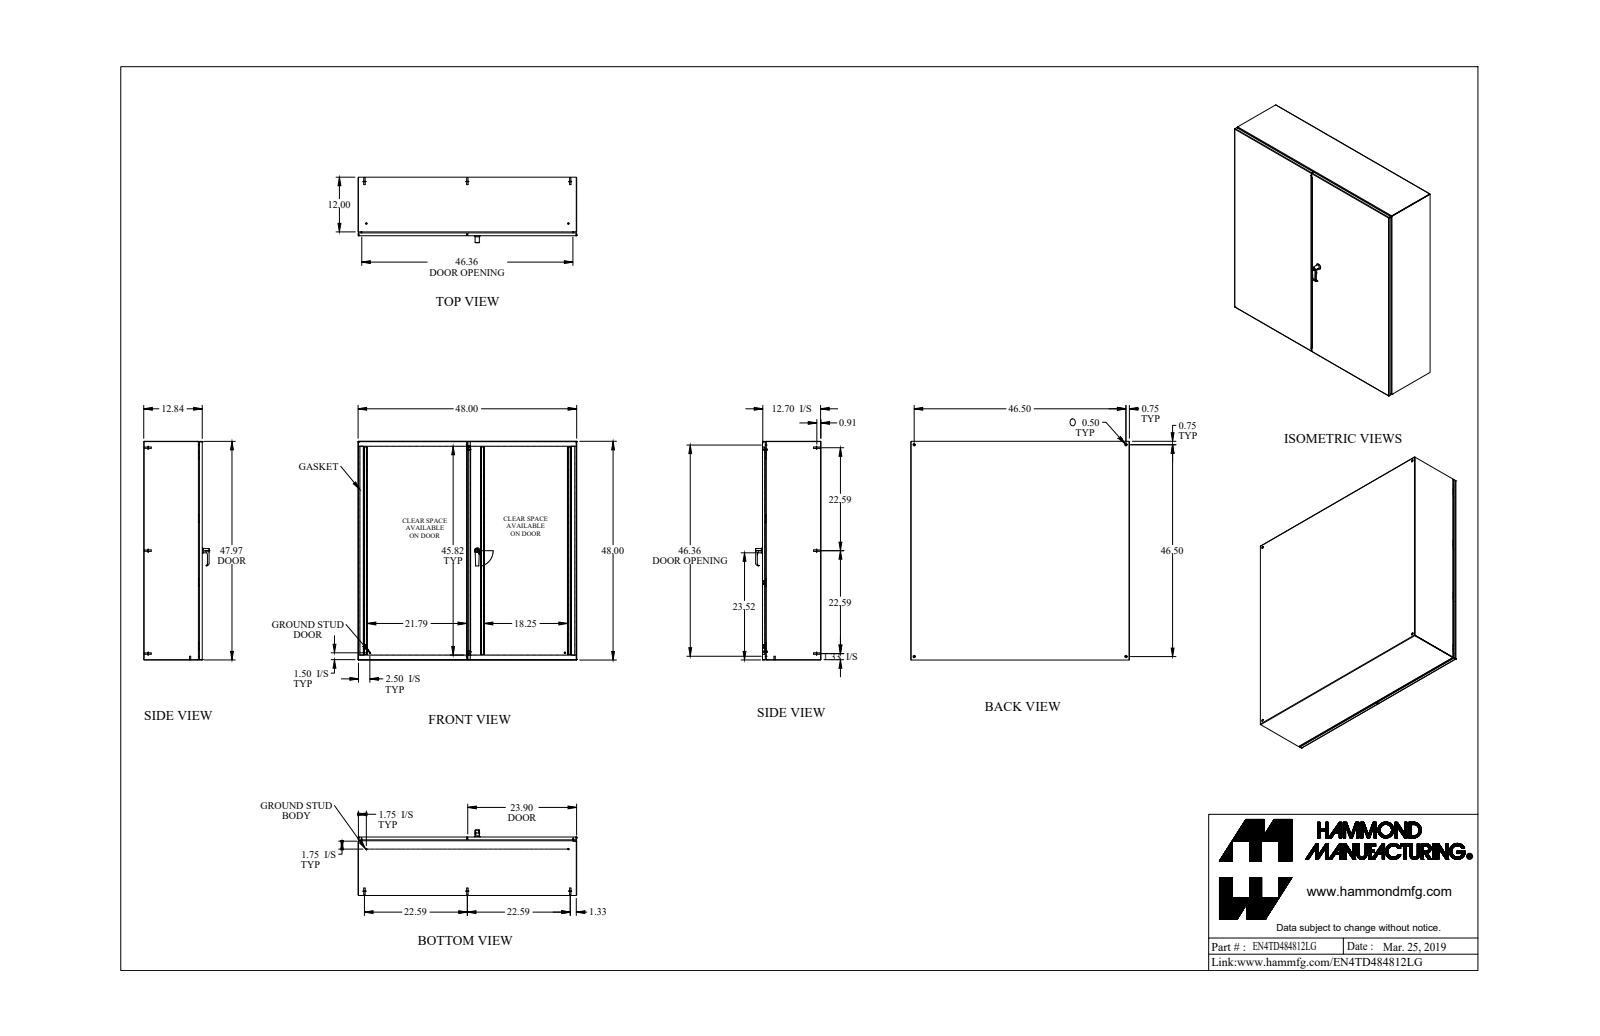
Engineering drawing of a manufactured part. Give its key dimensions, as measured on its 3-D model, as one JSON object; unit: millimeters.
{"part_name": "EN4TD484812LG", "step_written_by": "SolidWorks 2018 (AUTOMOTIVE_DESIGN)", "units": "millimeters", "bodies": {"solids": 97, "faces": 2415, "planar": 1058, "cylindrical": 882, "other": 475}, "overall_size": [1219.2, 1219.2, 365], "volume_mm3": 9829000, "surface_area_mm2": 10310000, "round_holes": [[5, 6], [4.5, 4], [12.7, 4], [6.1, 3], [6.1, 3], [6.4, 3], [6.7, 3], [4.4, 2], [6.5, 2], [6.6, 2], [8, 2], [10, 2]], "round_bosses_or_shafts": [[6.4, 12], [8, 10], [15.9, 8], [6.9, 8], [13, 4], [7.1, 4], [4, 4], [19.1, 3]], "partial_cylinders_radius": [[0.9, 26], [2.7, 26], [1.6, 24], [2.4, 20], [1.1, 18], [2.1, 18], [0.2, 16], [0.5, 16]], "face_to_face_distances": [1.8, 324.4, 322.5, 326.2, 1217.4, 1219.2, 1.8, 1215.5, 1215.5, 1217.4], "hole_center_spacings": [1181.1, 20, 459.6, 528.2, 654.2, 722.6, 797.2, 875]}
